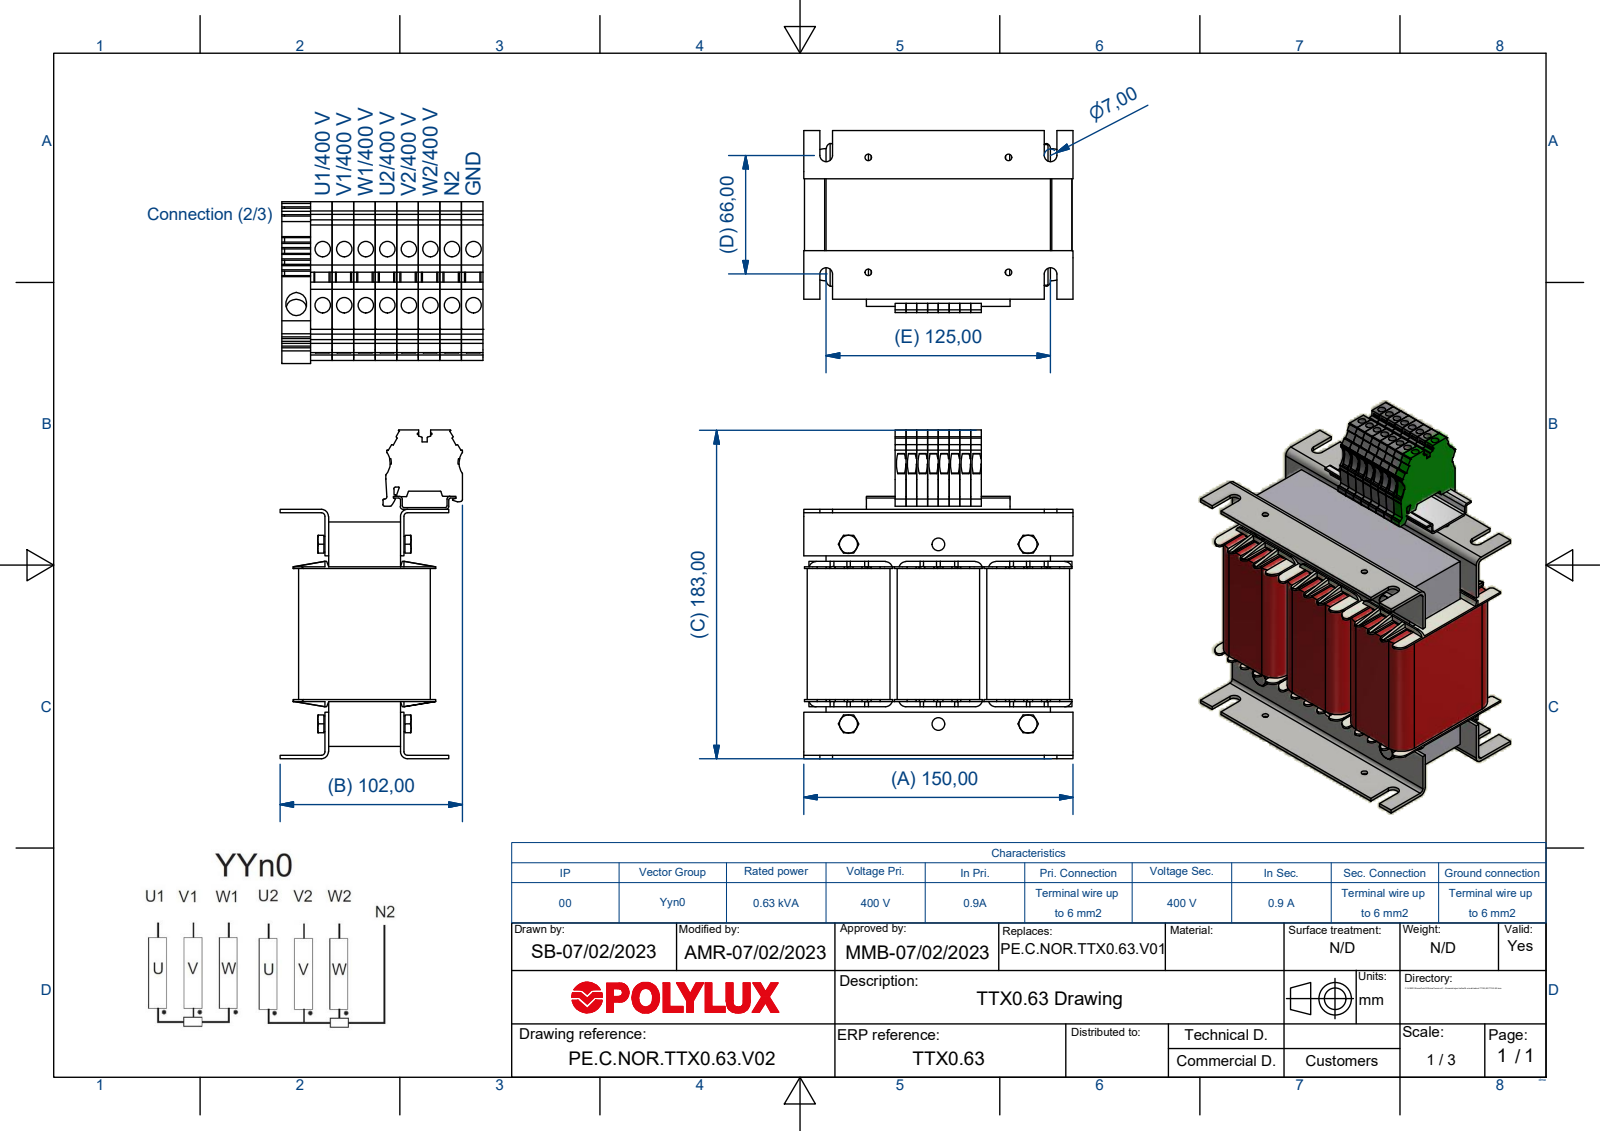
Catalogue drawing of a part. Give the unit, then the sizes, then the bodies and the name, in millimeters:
Units: millimetres
Overall size (bounding box): 183.15 × 150 × 101.5
Round holes (diameter × count): ⌀4.3 ×16, ⌀7 ×6, ⌀3.5 ×4
Round bosses / shafts (diameter × count): ⌀8.7 ×4, ⌀6 ×4, ⌀5.46 ×4
Partial cylindrical surfaces — rounded edges, fillets, slot ends (radius × count): R3 ×36, R2 ×16, R4 ×16, R24.01 ×16, R10 ×14, R0.1 ×12, R0.3 ×11, R1 ×10
Main face-to-face distances: 50, 100, 30, 1.75, 42, 2, 25, 41.75, 8, 40
Hole centre spacings: 6, 16.71, 12, 19.68, 18, 23.82, 15.6, 24
Volume: 1 101 000 mm³ · Surface area: 357 607 mm²
Bodies: 28 solids, 2210 faces (1488 planar, 658 cylindrical, 64 other)
Part name (STEP PRODUCT): TTX0.63; Carrete 25x40_Bobinado; Carrete 25x40 EI III; Bobina 25x40 (+6 more)
STEP written by: Autodesk Inventor 2018 (AUTOMOTIVE_DESIGN)
